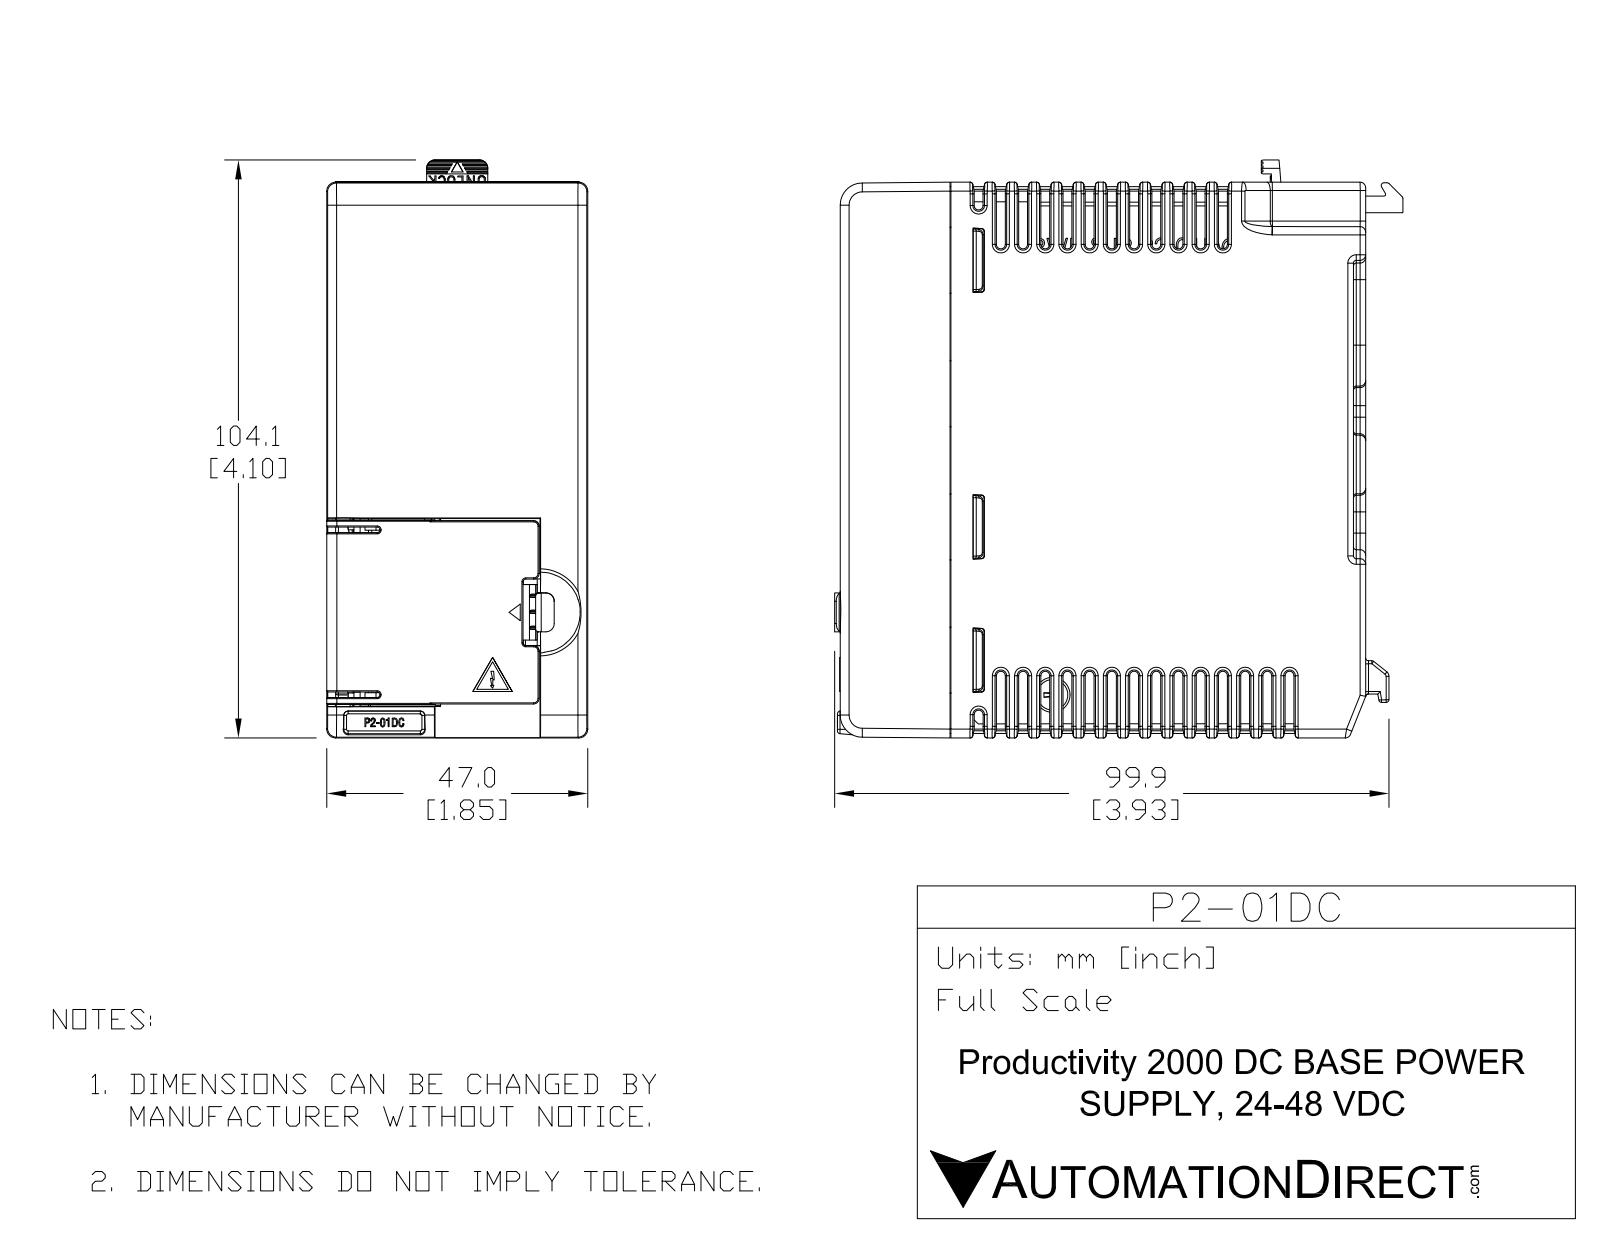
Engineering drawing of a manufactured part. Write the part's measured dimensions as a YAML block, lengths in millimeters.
part_name: "P2-01DC d fXT nc -AC"
step_written_by: "SolidWorks 2017 (AUTOMOTIVE_DESIGN)"
units: millimeters
bodies: {solids: 2, faces: 3888, planar: 1840, cylindrical: 1007, other: 1041}
overall_size: [104.1, 102.4, 47]
volume: 367400
surface_area: 70390
round_holes:
  - {diameter: 0.8, count: 7}
  - {diameter: 3.2, count: 2}
  - {diameter: 3.3, count: 2}
  - {diameter: 1, count: 1}
  - {diameter: 2, count: 1}
  - {diameter: 2.2, count: 1}
round_bosses_or_shafts:
  - {diameter: 5.6, count: 2}
  - {diameter: 2.8, count: 2}
  - {diameter: 10.6, count: 1}
  - {diameter: 2.5, count: 1}
partial_cylinders:
  - {radius: 0.5, count: 254}
  - {radius: 1, count: 90}
  - {radius: 0.2, count: 51}
  - {radius: 0.4, count: 24}
  - {radius: 1.5, count: 14}
  - {radius: 1.6, count: 10}
  - {radius: 0.9, count: 4}
  - {radius: 1.3, count: 4}
face_to_face_distances: [1.6, 45.4, 10.8, 3.9, 7.8, 47, 11.8, 15.7, 83.9, 94.6]
hole_center_spacings: [13, 5.1, 2.5, 7.9, 10.5, 15.5, 18.1, 26]
